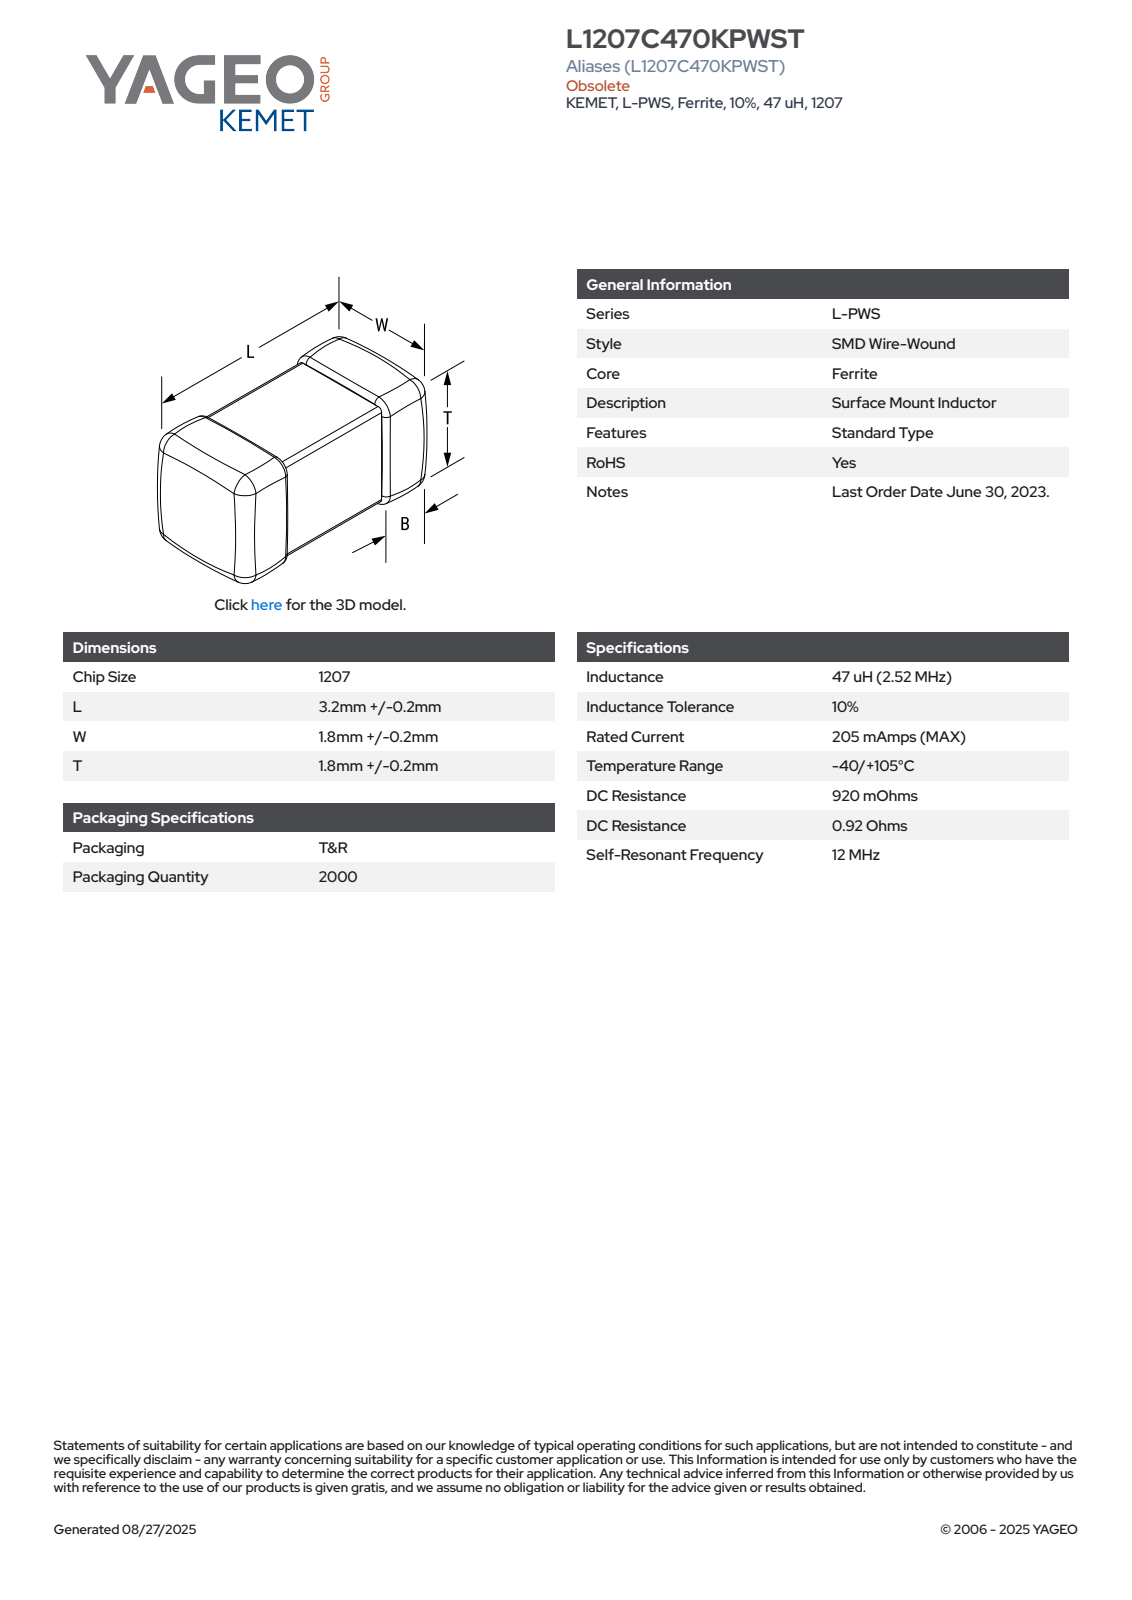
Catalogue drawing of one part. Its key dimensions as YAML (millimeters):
part_name: "IS_KC_1207_L3.4W2T2LL0.8"
step_written_by: "SolidWorks 2014 (AUTOMOTIVE_DESIGN)"
units: millimeters
bodies: {solids: 4, faces: 73, planar: 73, cylindrical: 0, other: 0}
overall_size: [3.4, 2, 2]
volume: 13
surface_area: 36
face_to_face_distances: [1.97, 1.94, 2, 3.4, 0.8, 2.6, 1.8, 0.78, 0.75, 1.58]
